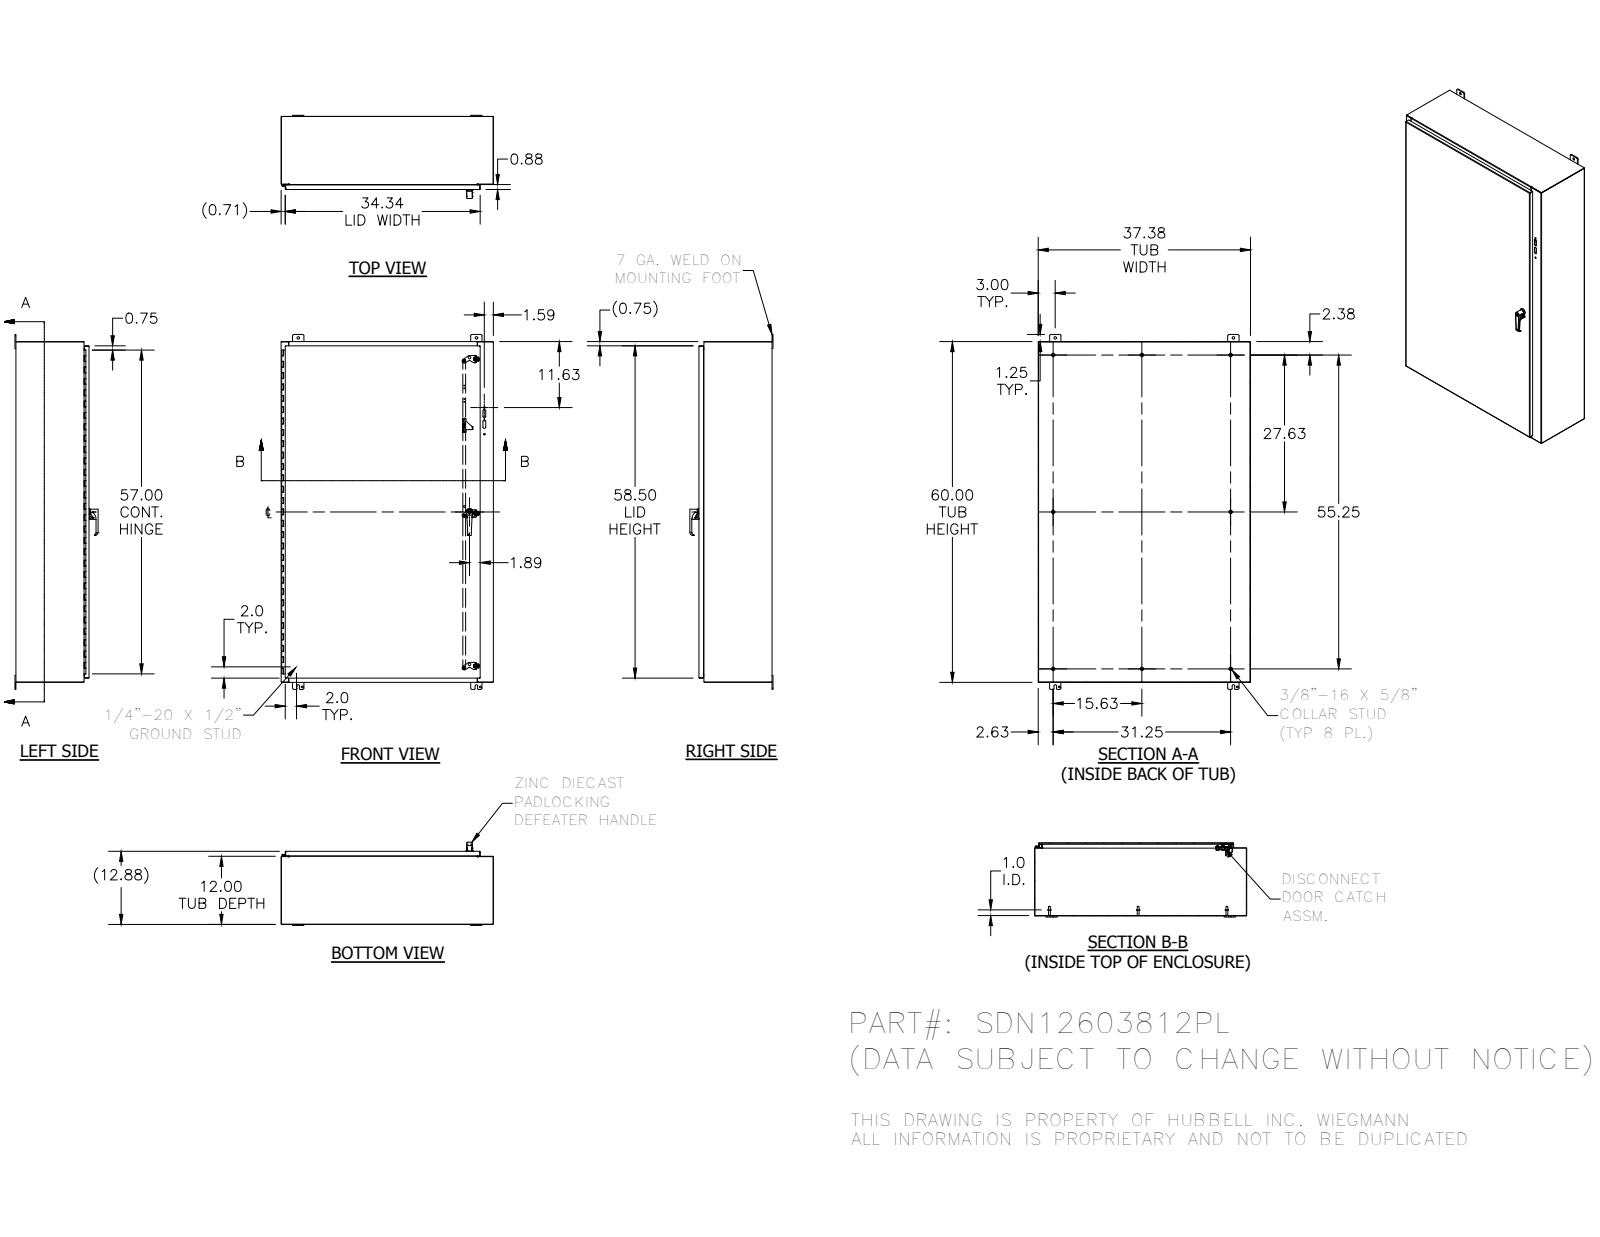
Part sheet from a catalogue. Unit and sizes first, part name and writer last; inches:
Units: inches
Overall size (bounding box): 62.5 × 37.375 × 14.649
Round holes (diameter × count): ⌀0.145 ×6, ⌀0.313 ×4, ⌀0.32 ×4, ⌀0.438 ×4, ⌀0.196 ×3, ⌀0.211 ×3, ⌀0.22 ×3, ⌀0.313 ×3, ⌀0.45 ×3, ⌀0.156 ×2, ⌀0.281 ×2, ⌀0.307 ×2
Round bosses / shafts (diameter × count): ⌀0.33 ×11, ⌀0.625 ×10, ⌀0.437 ×6, ⌀0.3 ×6, ⌀0.225 ×6, ⌀0.25 ×4, ⌀0.19 ×4, ⌀0.75 ×3
Partial cylindrical surfaces — rounded edges, fillets, slot ends (radius × count): R0.02 ×38, R0.012 ×30, R0.025 ×24, R0.25 ×23, R0.125 ×21, R0.031 ×18, R0.105 ×18, R0.094 ×6
Main face-to-face distances: 0.074, 12.801, 12.727, 12.875, 37.301, 59.926, 37.227, 37.375, 11.926, 0.875
Hole centre spacings: 54, 26.844, 27.156, 1.593, 31.375, 60, 67.708, 0.5
Volume: 553.3 in³ · Surface area: 14 867 in²
Bodies: 64 solids, 1997 faces (1084 planar, 659 cylindrical, 254 other)
Part name (STEP PRODUCT): SDN12603812PL; SDN12603812PLBLR; 3889; 34840 (+8 more)
STEP written by: Autodesk Inventor 2012 (AUTOMOTIVE_DESIGN)
